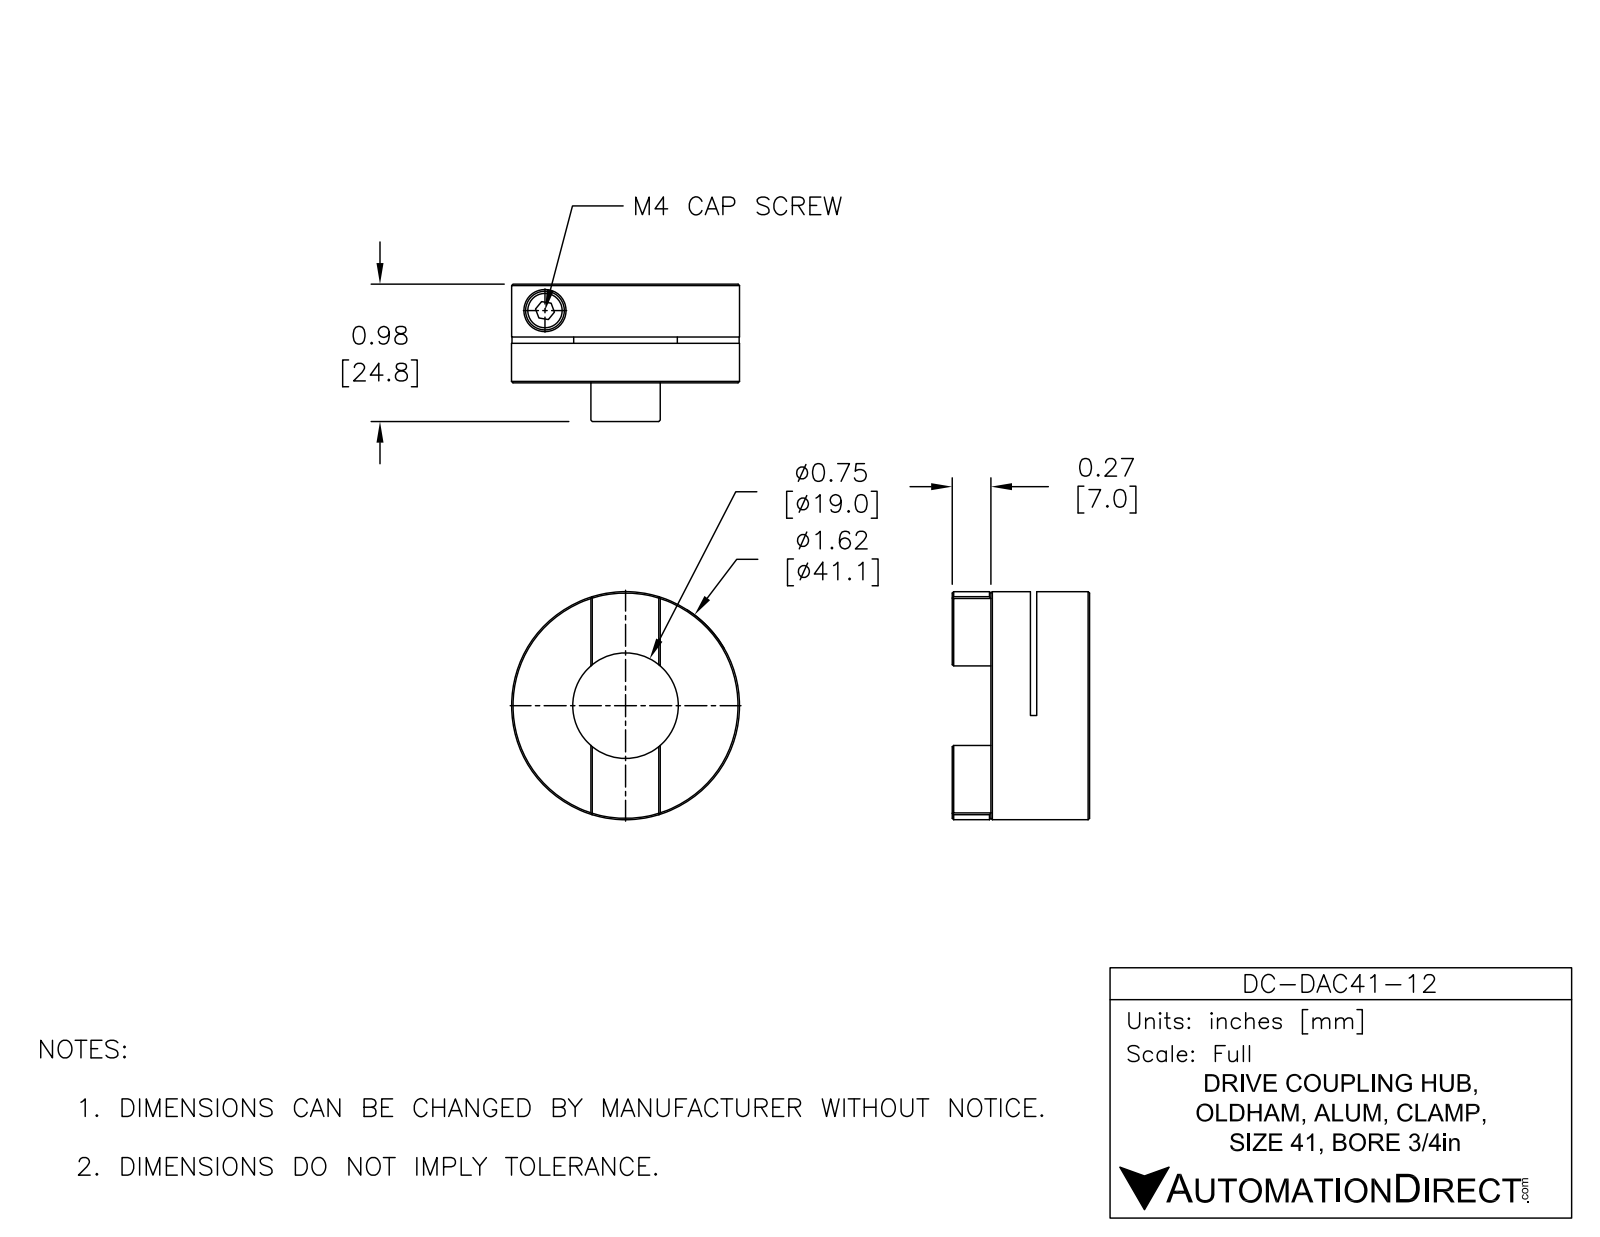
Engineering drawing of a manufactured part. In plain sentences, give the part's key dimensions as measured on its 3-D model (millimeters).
The part is named "DC-DAC41-12". Its 3-D file was written by "SolidWorks 2015 (AUTOMOTIVE_DESIGN)". It is 1 solid with 51 faces: 27 planar, 15 cylindrical and 9 other. Overall it measures 41.15 by 41.15 by 24.78 millimeters. Its volume is 19 106 cubic millimeters and its surface area 7 768 square millimeters. Round holes: 1 of diameter 3.99, 1 of diameter 7.62, 1 of diameter 19.05. Round bosses or shafts: 1 of diameter 41.15. Partial cylindrical surfaces (rounded edges, fillets, slot ends): 1 of radius 22.23. The main face-to-face distances are 17.8, 7.14, 10.66, 8.28, 1.14, 9.52, 6.97, 14.11, 15.25, 24.77.
